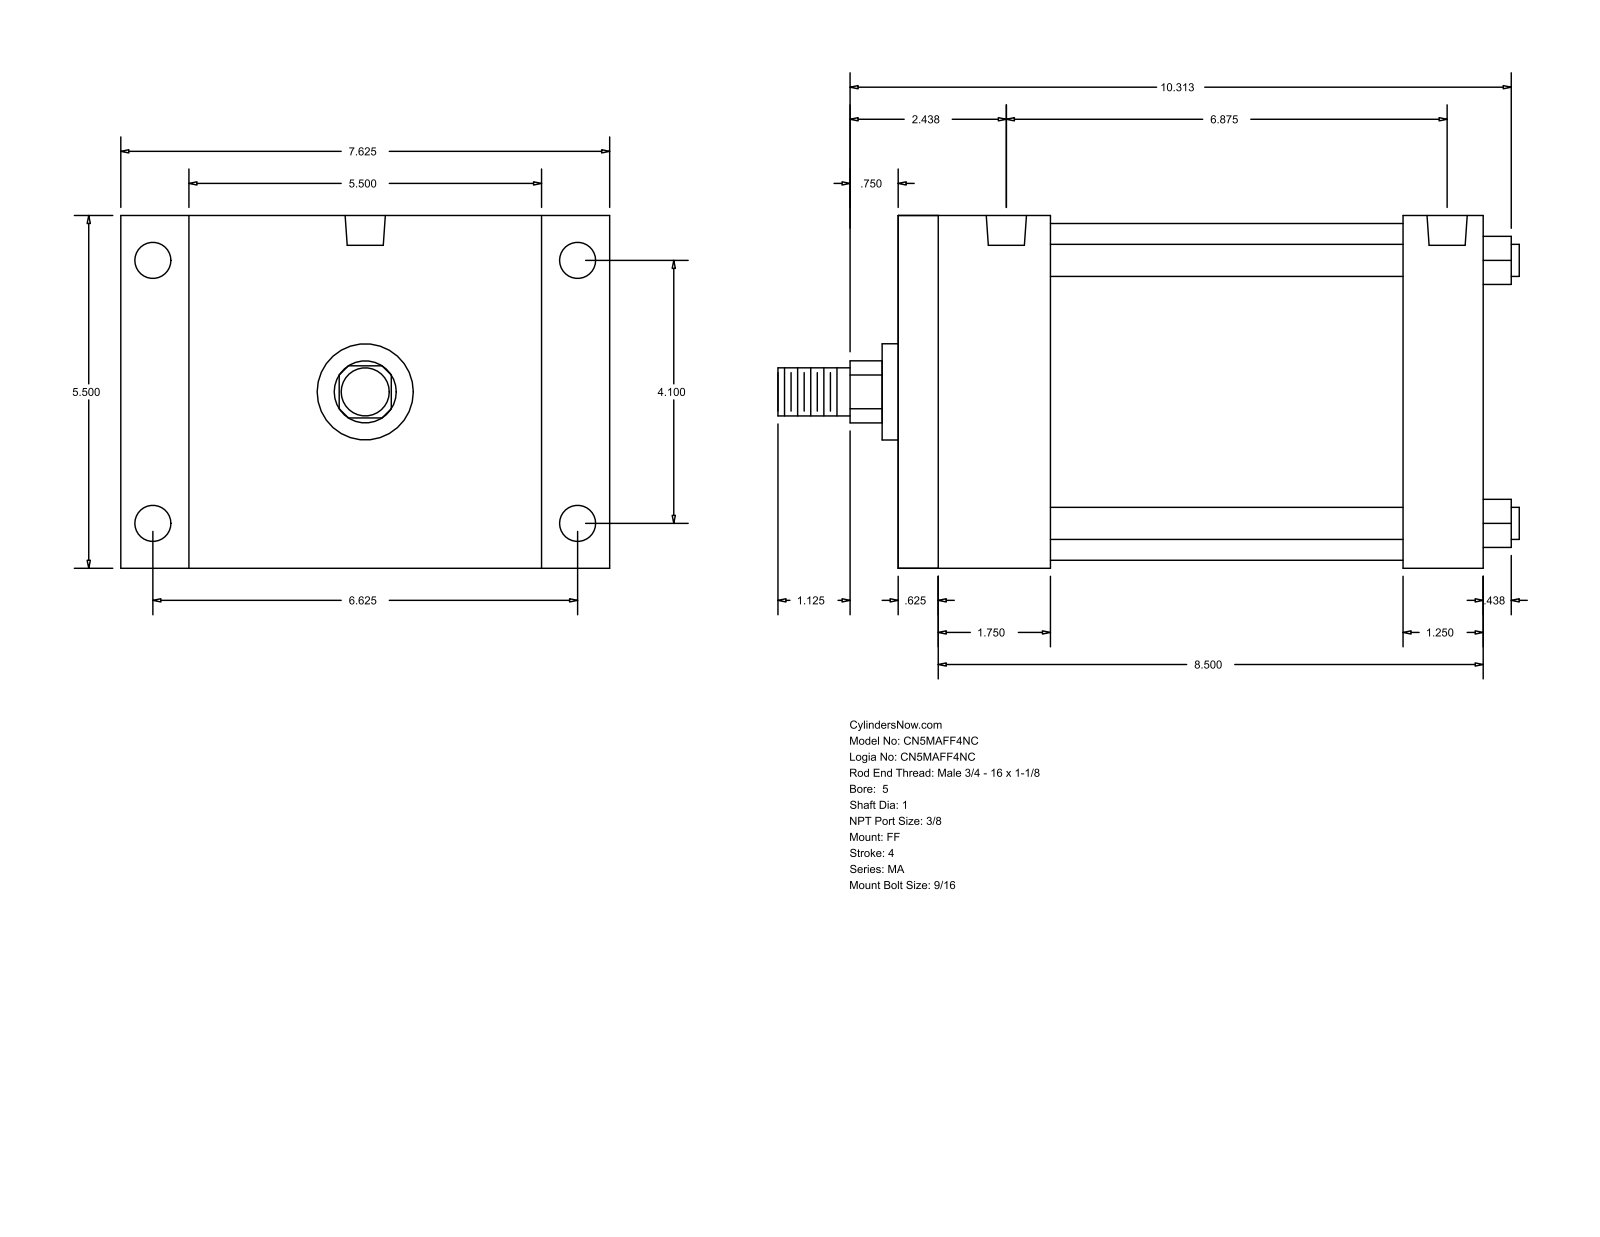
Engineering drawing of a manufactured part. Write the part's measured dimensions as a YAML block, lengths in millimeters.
part_name: "MA_FF__0500_1"
step_written_by: "GSSL Pune (CONFIG_CONTROL_DESIGN)"
units: millimeters
bodies: {solids: 0, faces: 92, planar: 64, cylindrical: 28, other: 0}
overall_size: [293.69, 193.68, 139.7]
round_holes:
  - {diameter: 11.11, count: 4}
  - {diameter: 14.29, count: 4}
  - {diameter: 15.93, count: 2}
round_bosses_or_shafts:
  - {diameter: 12.7, count: 4}
  - {diameter: 133.35, count: 1}
  - {diameter: 38.1, count: 1}
  - {diameter: 25.4, count: 1}
  - {diameter: 19.05, count: 1}
partial_cylinders:
  - {radius: 12.29, count: 1}
face_to_face_distances: [139.7, 231.77, 15.87, 215.9, 200.02, 184.15, 31.75, 60.33, 44.46, 139.69]
hole_center_spacings: [4.76, 104.14, 165.11, 168.28, 169.87, 197.9, 174.63]
